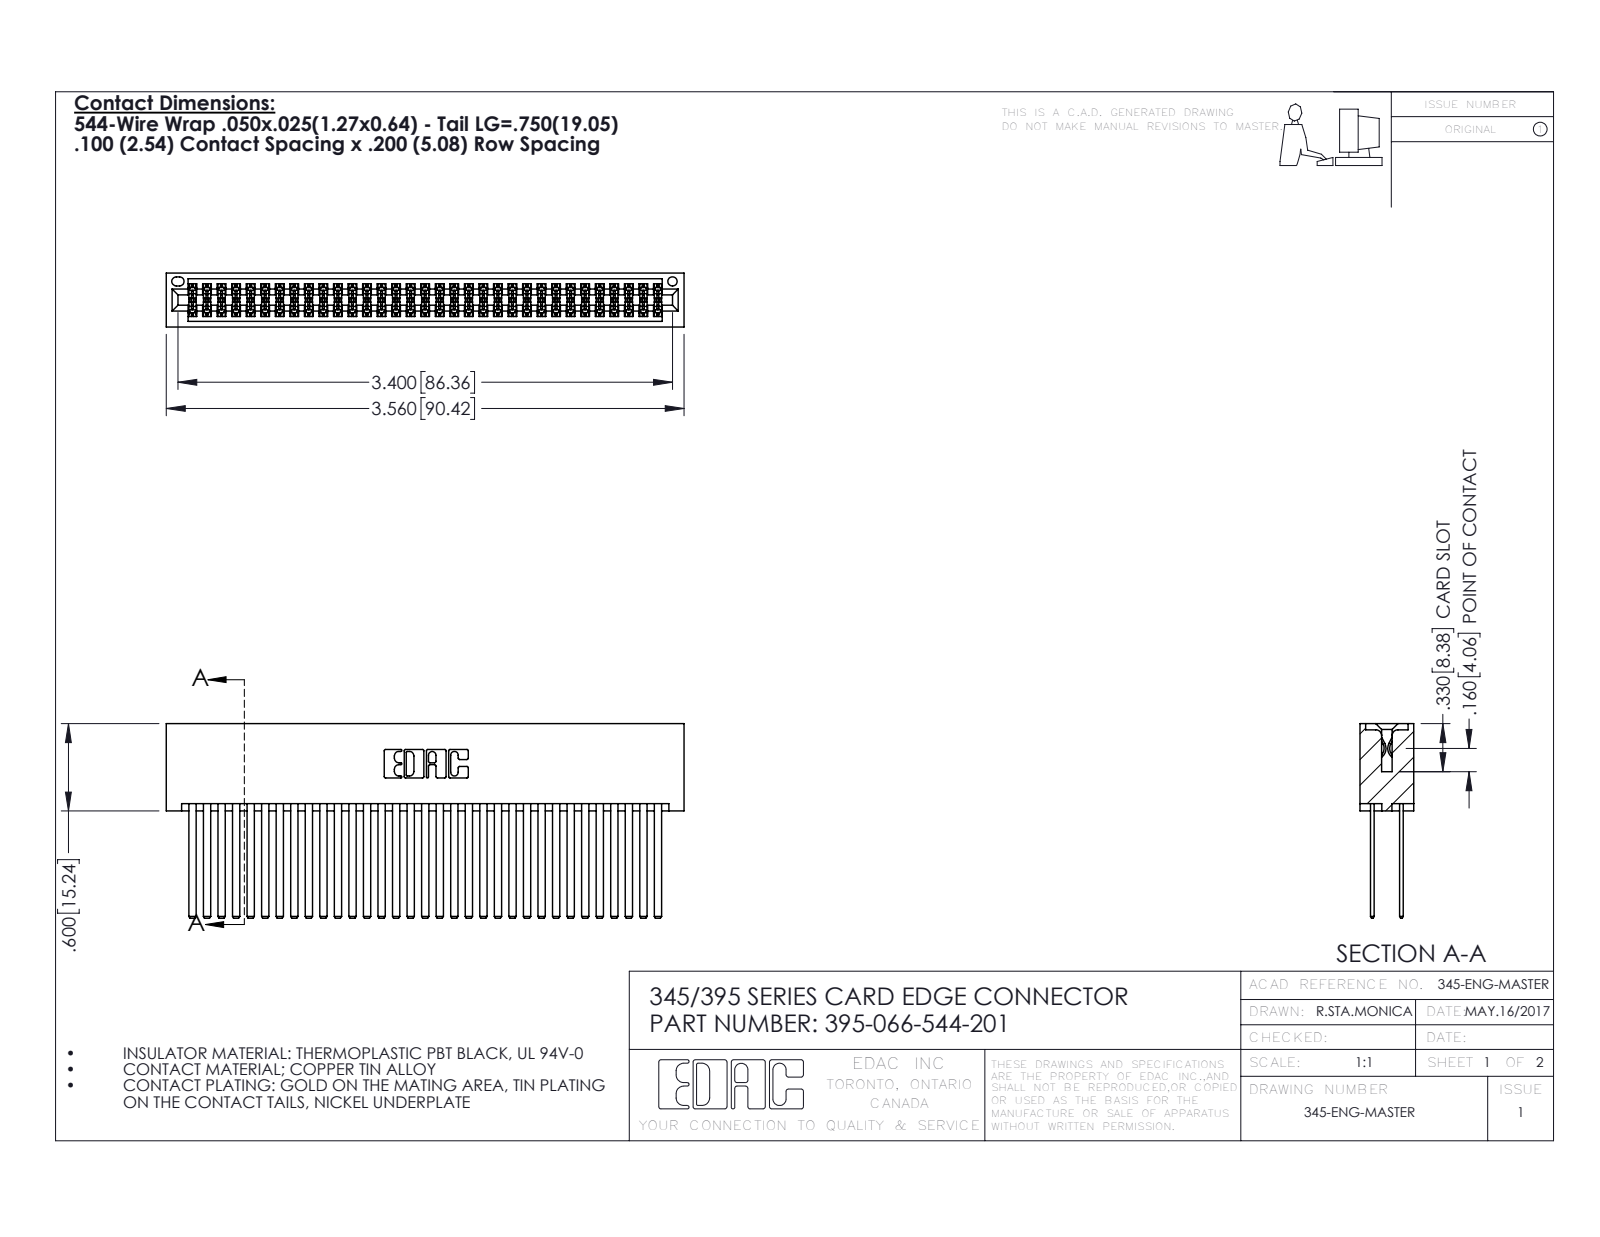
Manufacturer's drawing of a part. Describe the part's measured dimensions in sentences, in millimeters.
The part is named "345-292-001_345-293-144; 395-066-544-201; 345 Part_No Mounting Lugs". Its 3-D file was written by "SolidWorks 2016 (CONFIG_CONTROL_DESIGN)". It is 67 solids with 3022 faces: 1990 planar, 1032 cylindrical and 0 other. Overall it measures 90.4 by 34 by 9.4 millimeters. Its volume is 10 200 cubic millimeters and its surface area 17 980 square millimeters. Round holes: 1 of diameter 1.6. Partial cylindrical surfaces (rounded edges, fillets, slot ends): 99 of radius 0.2, 22 of radius 0.3, 6 of radius 0.2, 6 of radius 0.8, 3 of radius 0.7, 2 of radius 0.4, 2 of radius 0.5, 2 of radius 0.6. The main face-to-face distances are 5.1, 0.6, 7.6, 1.8, 2.5, 6.9, 5.7, 4.4, 9.4, 1.3.
